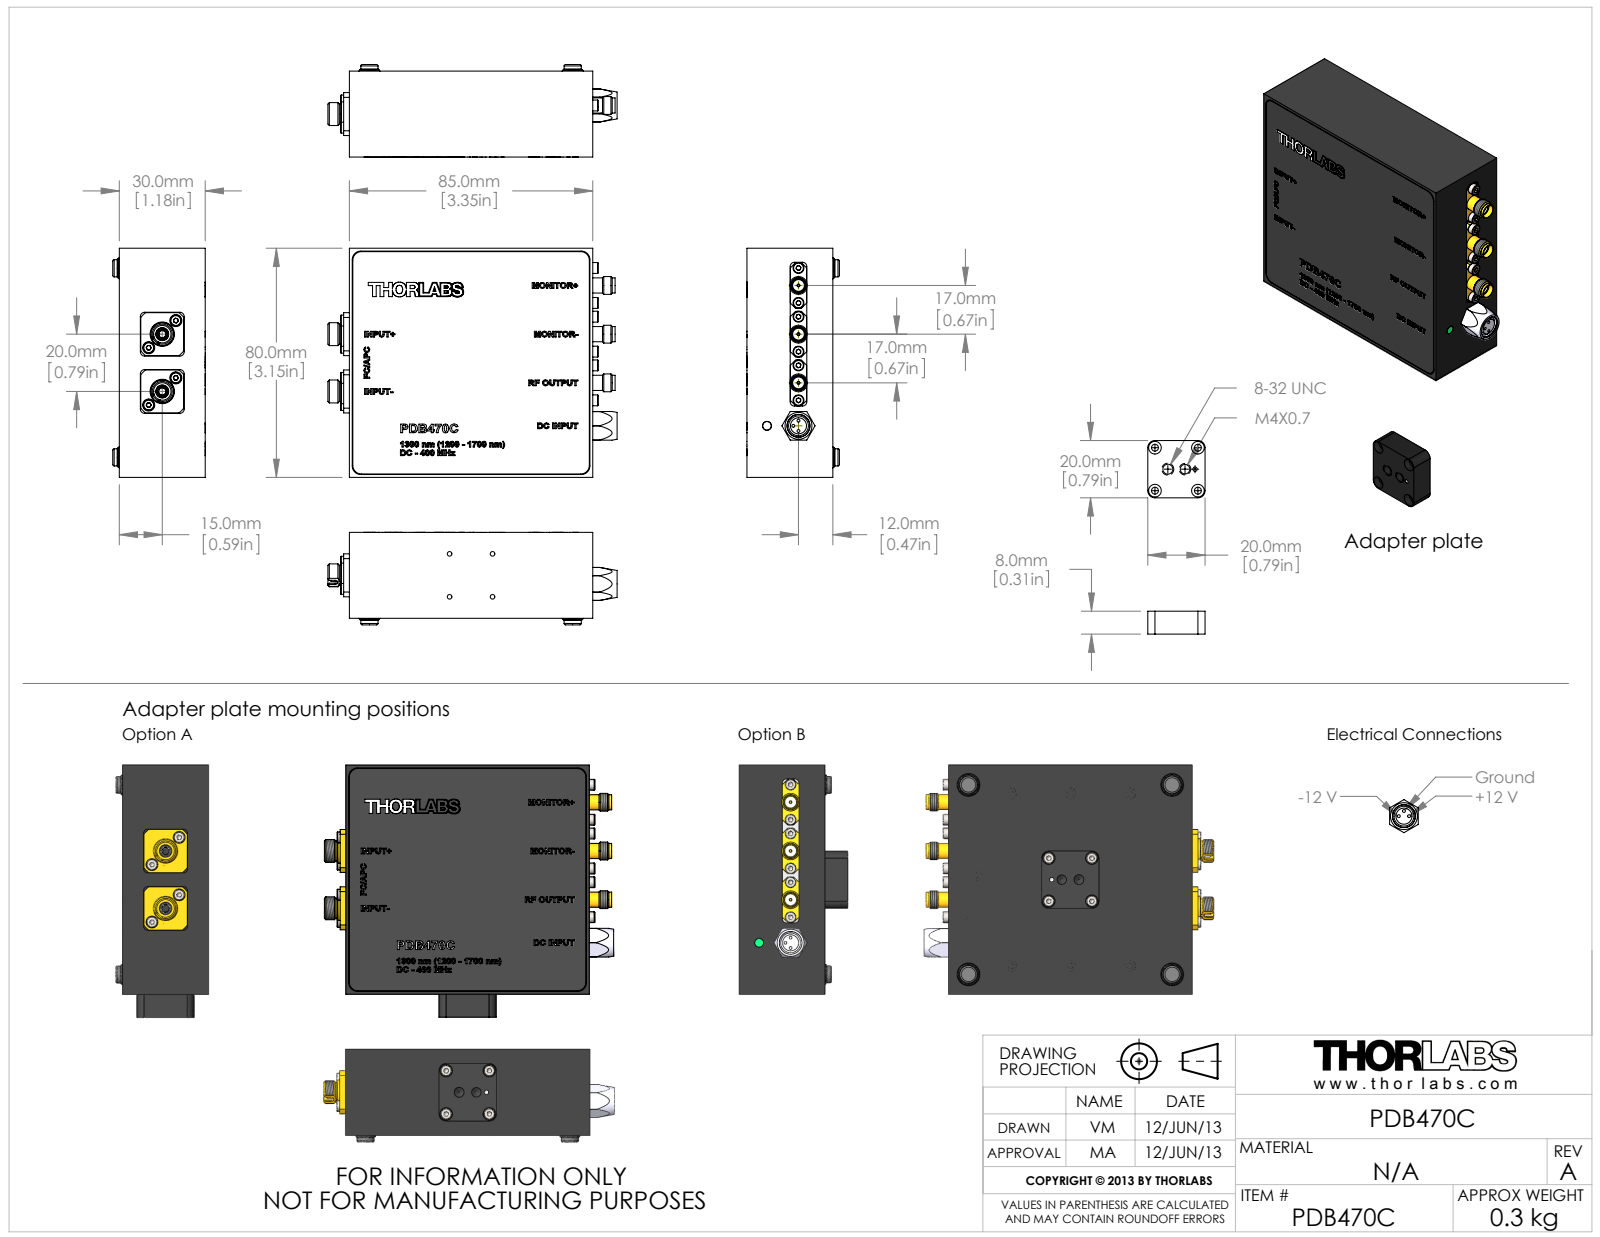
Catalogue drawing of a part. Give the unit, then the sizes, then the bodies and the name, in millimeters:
Units: millimetres
Overall size (bounding box): 101 × 88 × 38
Round holes (diameter × count): ⌀1.6 ×29, ⌀2.4 ×8, ⌀4.4 ×8, ⌀8 ×7, ⌀2.6 ×6, ⌀1.5 ×4, ⌀0.8 ×3, ⌀1 ×3, ⌀4.1 ×3, ⌀4.2 ×3, ⌀4.7 ×3, ⌀3.2 ×2
Round bosses / shafts (diameter × count): ⌀3.8 ×25, ⌀2 ×25, ⌀4.2 ×8, ⌀2.3 ×8, ⌀6 ×6, ⌀1.57 ×4, ⌀6.22 ×3, ⌀5.3 ×3
Partial cylindrical surfaces — rounded edges, fillets, slot ends (radius × count): R1.5 ×12, R3 ×12, R5 ×10, R2.5 ×8, R1.02 ×4, R8 ×3, R9.5 ×2, R5.75 ×1
Main face-to-face distances: 30, 29.7, 6, 23.7, 24, 5.5, 80, 85, 2, 74.5
Hole centre spacings: 15, 8.75, 12.9, 6.1, 17, 2.83, 7.57, 10.9
Volume: 89 116 mm³ · Surface area: 58 103 mm²
Bodies: 84 solids, 3098 faces (1768 planar, 542 cylindrical, 788 other)
Part name (STEP PRODUCT): M0092-0699 Grundkörper PDB480C-AC Rev C; FCAPCBuchse-03a-Senko switchable (Typ321-102); FCAPCBuchse-03-Senko switchable (Typ321-102); Socket Head Cap Screw_DIN_DIN 912 M2 x 3 --- 3N (+8 more)
STEP written by: SolidWorks 2012 (AUTOMOTIVE_DESIGN)
